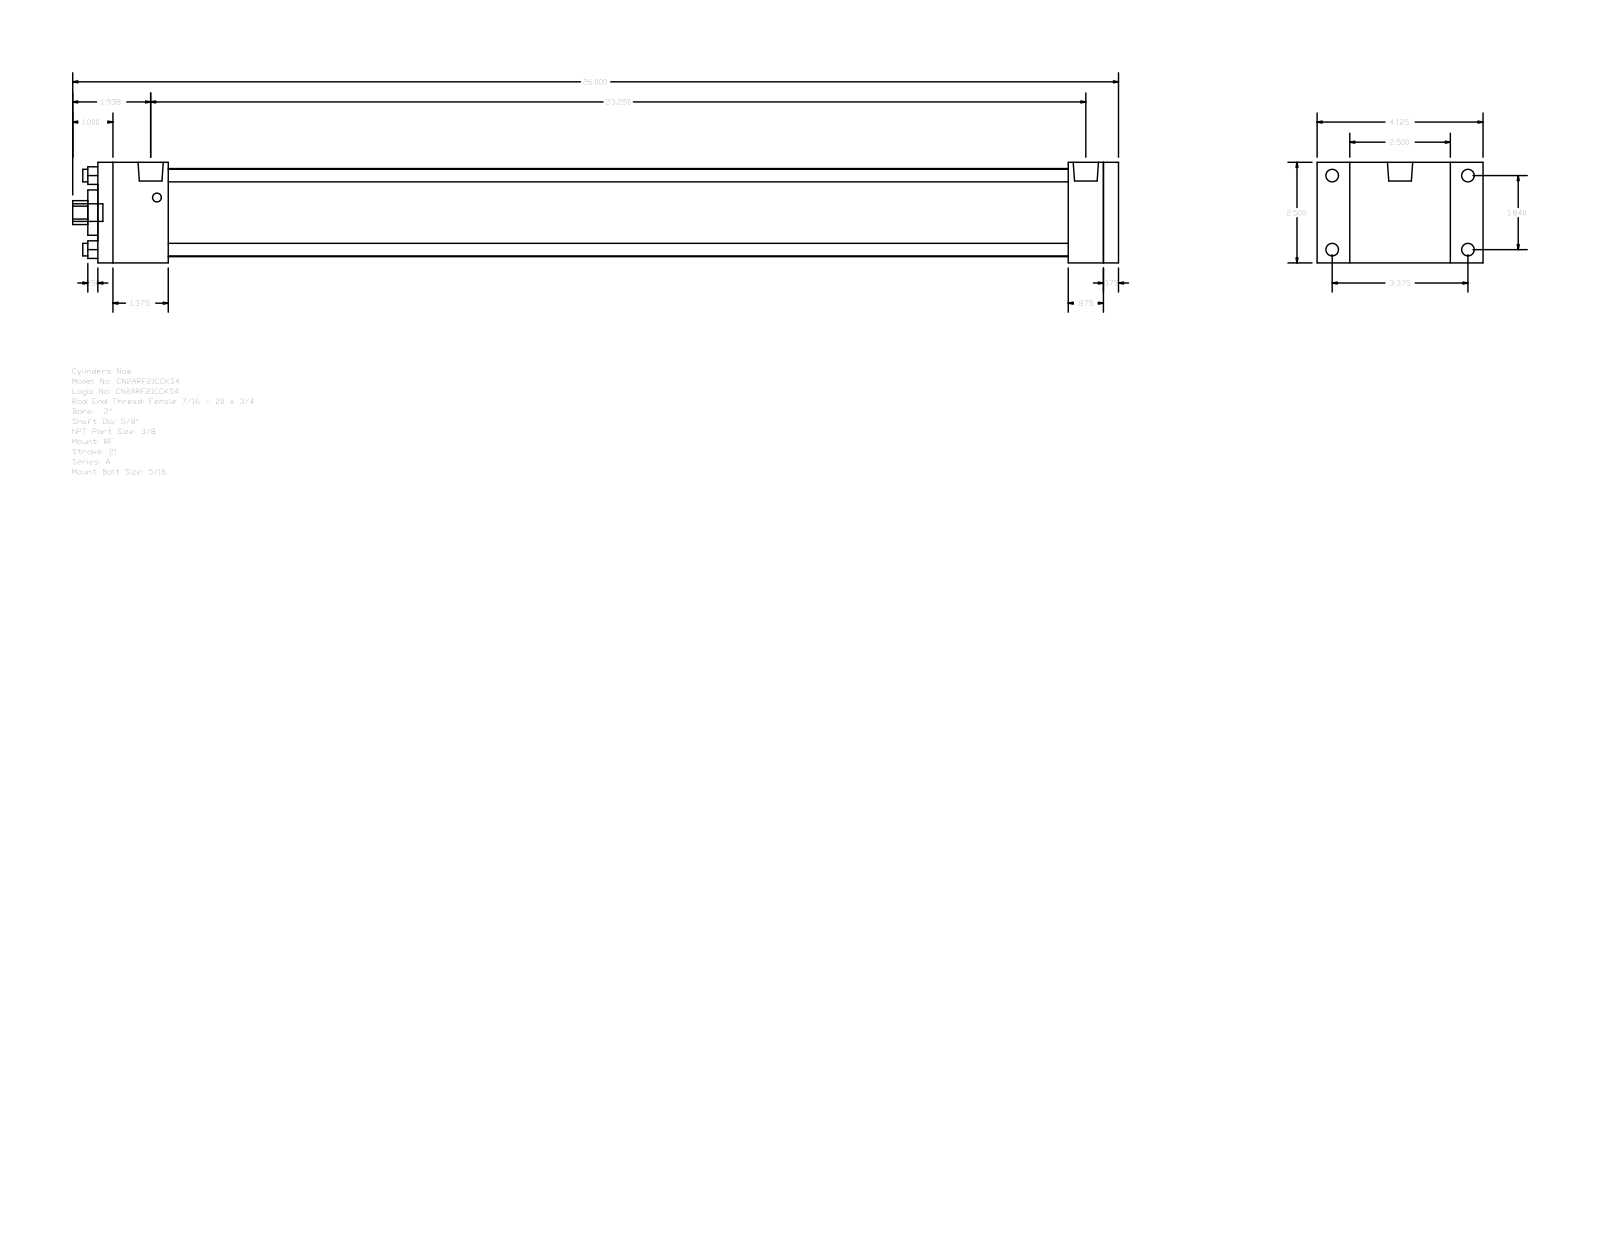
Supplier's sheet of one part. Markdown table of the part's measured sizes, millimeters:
| quantity | value |
| --- | --- |
| part name | A_RF__0200_0.625 |
| STEP written by | GSSL Pune (CONFIG_CONTROL_DESIGN) |
| units | millimeters |
| bodies | 0 solids, 92 faces (64 planar, 28 cylindrical, 0 other) |
| overall size | 660.4 × 104.78 × 63.5 |
| round holes (diameter × count) | 7.94 × 4, 15.88 × 1, 28.57 × 1, 55.63 × 1 |
| round bosses / shafts (diameter × count) | 7.94 × 4, 5.56 × 4, 15.93 × 2, 11.11 × 1 |
| partial cylindrical surfaces (radius × count) | 7.54 × 1 |
| main face-to-face distances | 63.5, 644.52, 9.52, 635, 44.45, 590.55, 600.07, 612.77, 568.32, 22.23 |
| hole center spacings | 33.05, 46.74, 66.1 |
